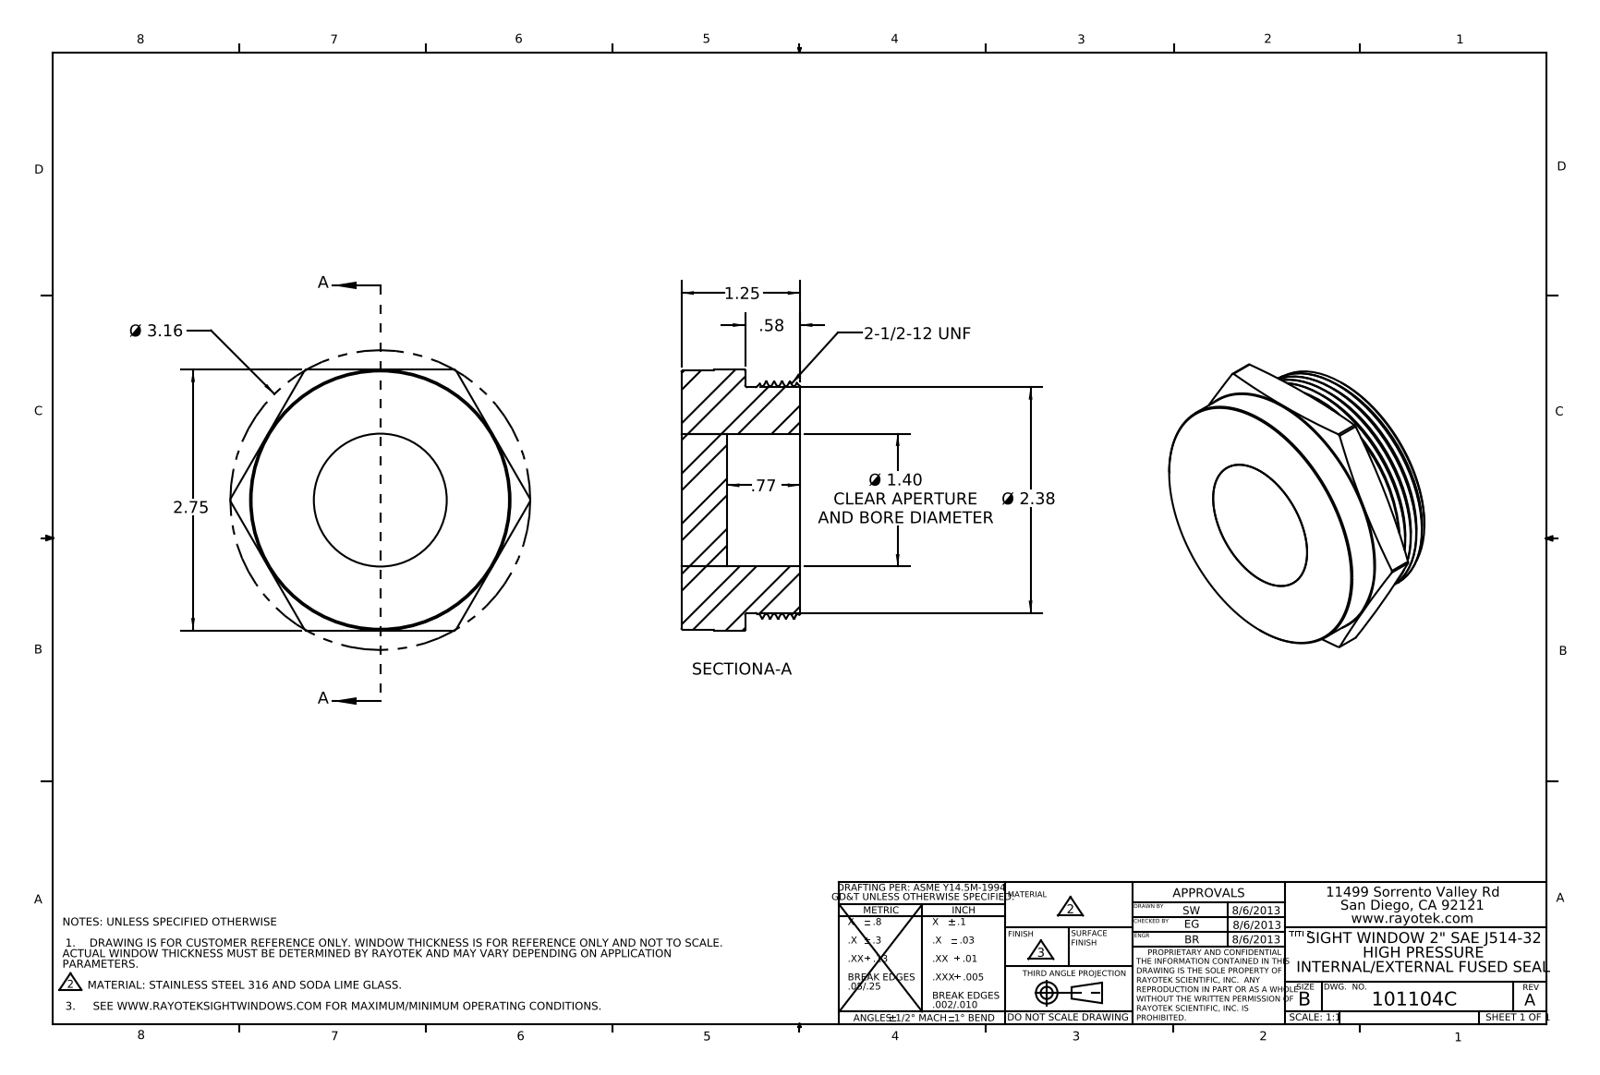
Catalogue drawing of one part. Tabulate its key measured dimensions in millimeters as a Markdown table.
| quantity | value |
| --- | --- |
| part name | 403104 |
| STEP written by | SolidWorks 2012 (AUTOMOTIVE_DESIGN) |
| units | millimeters |
| bodies | 2 solids, 56 faces (11 planar, 24 cylindrical, 21 other) |
| overall size | 80.3 × 69.9 × 31.8 |
| volume | 92 310 mm³ |
| surface area | 21 360 mm² |
| round holes (diameter × count) | 35.6 × 1 |
| round bosses / shafts (diameter × count) | 69.5 × 1, 63.5 × 1, 60.5 × 1 |
| partial cylindrical surfaces (radius × count) | 40.2 × 1 |
| main face-to-face distances | 31.8, 19.6, 12.2, 14.7, 4.8, 17, 69.9, 69.9 |
